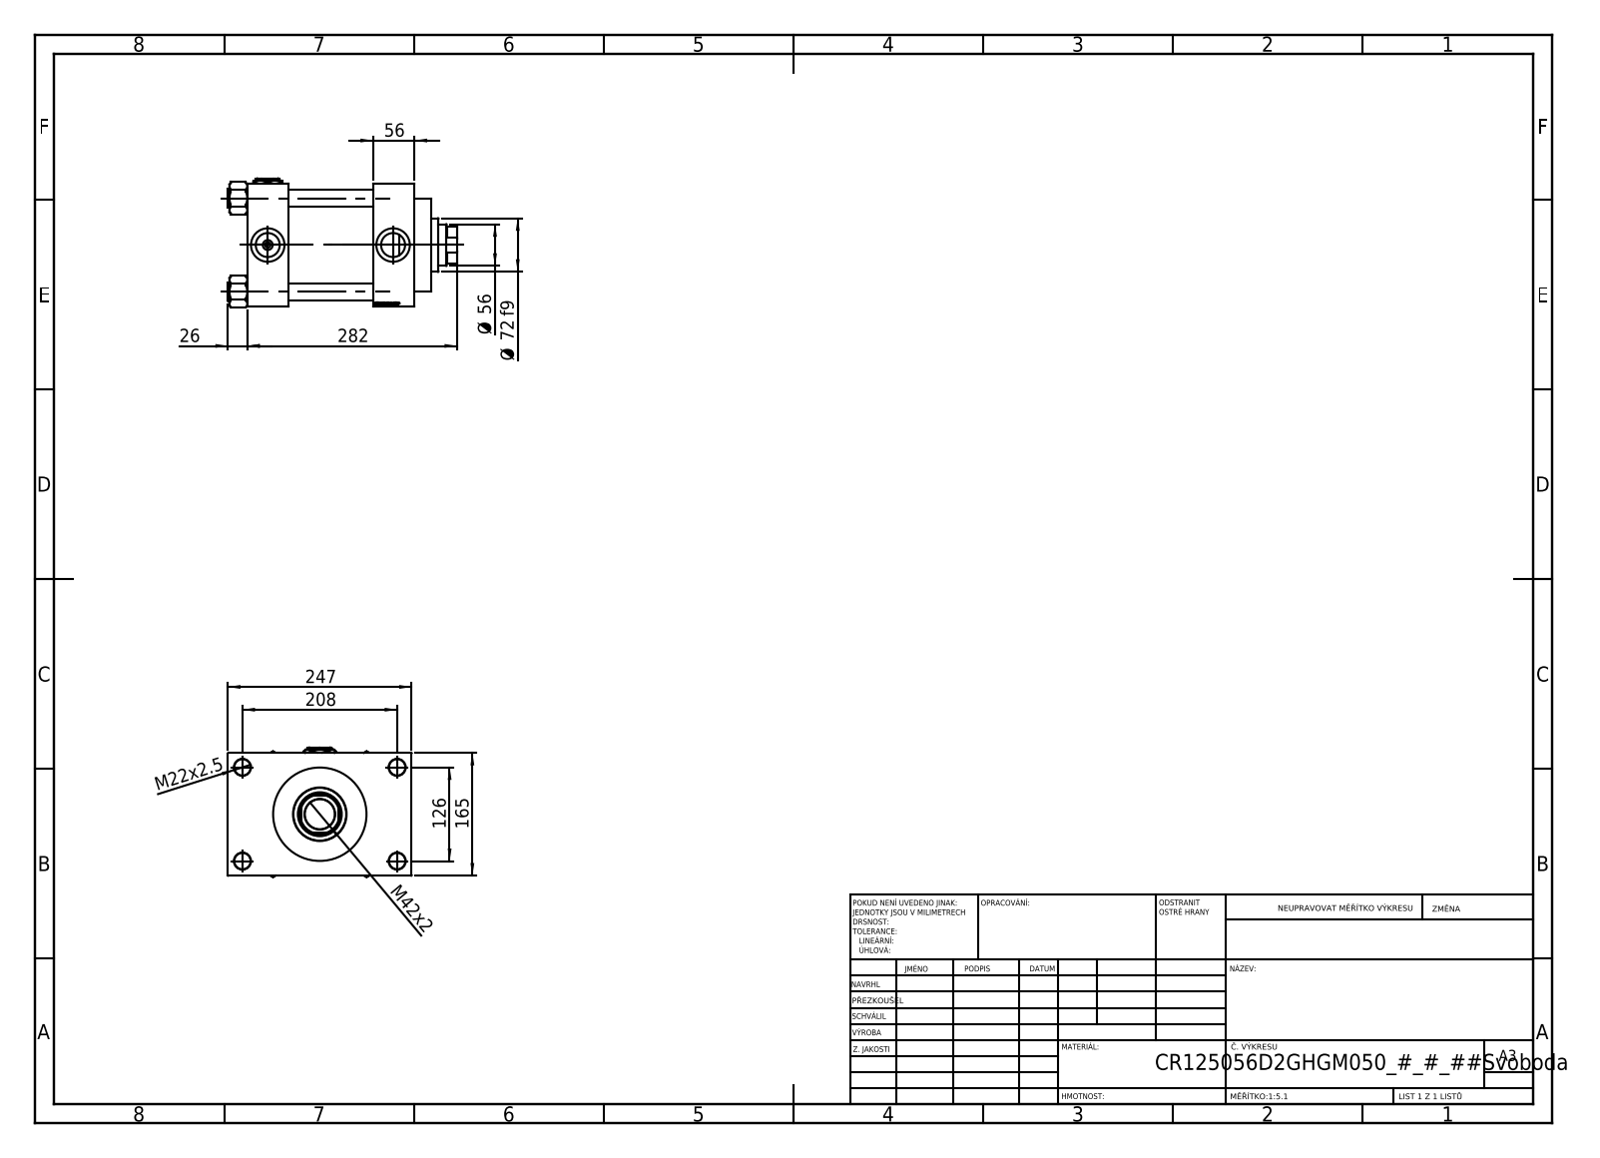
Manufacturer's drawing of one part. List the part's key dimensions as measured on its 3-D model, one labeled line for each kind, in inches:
Part name (STEP PRODUCT): V215CR_D_Body; V215CR_D_TYCINKA; Zatka_pro_OIL_PORT; NUT_M5_D (+2 more)
STEP written by: SolidWorks 2019 (CONFIG_CONTROL_DESIGN)
Units: inches
Bodies: 12 solids, 1201 faces (568 planar, 93 cylindrical, 540 other)
Overall size (bounding box): 12.126 × 9.724 × 6.853
Volume: 309.8 in³ · Surface area: 895.3 in²
Round holes (diameter × count): ⌀0.866 ×8, ⌀0.276 ×3, ⌀1.269 ×3, ⌀1.772 ×3, ⌀1.594 ×1, ⌀2.205 ×1, ⌀2.323 ×1, ⌀3.78 ×1, ⌀4.921 ×1, ⌀4.941 ×1
Round bosses / shafts (diameter × count): ⌀0.984 ×4, ⌀5.157 ×1, ⌀2.835 ×1
Partial cylindrical surfaces — rounded edges, fillets, slot ends (radius × count): R1.063 ×1
Main face-to-face distances: 4.488, 6.496, 6.654, 2.165, 6.693, 2.205, 8.858, 1.614, 9.724, 2.52
Hole centre spacings: 1.616, 3.505, 4.787, 4.957, 5.215, 6.573, 8.233, 4.961
